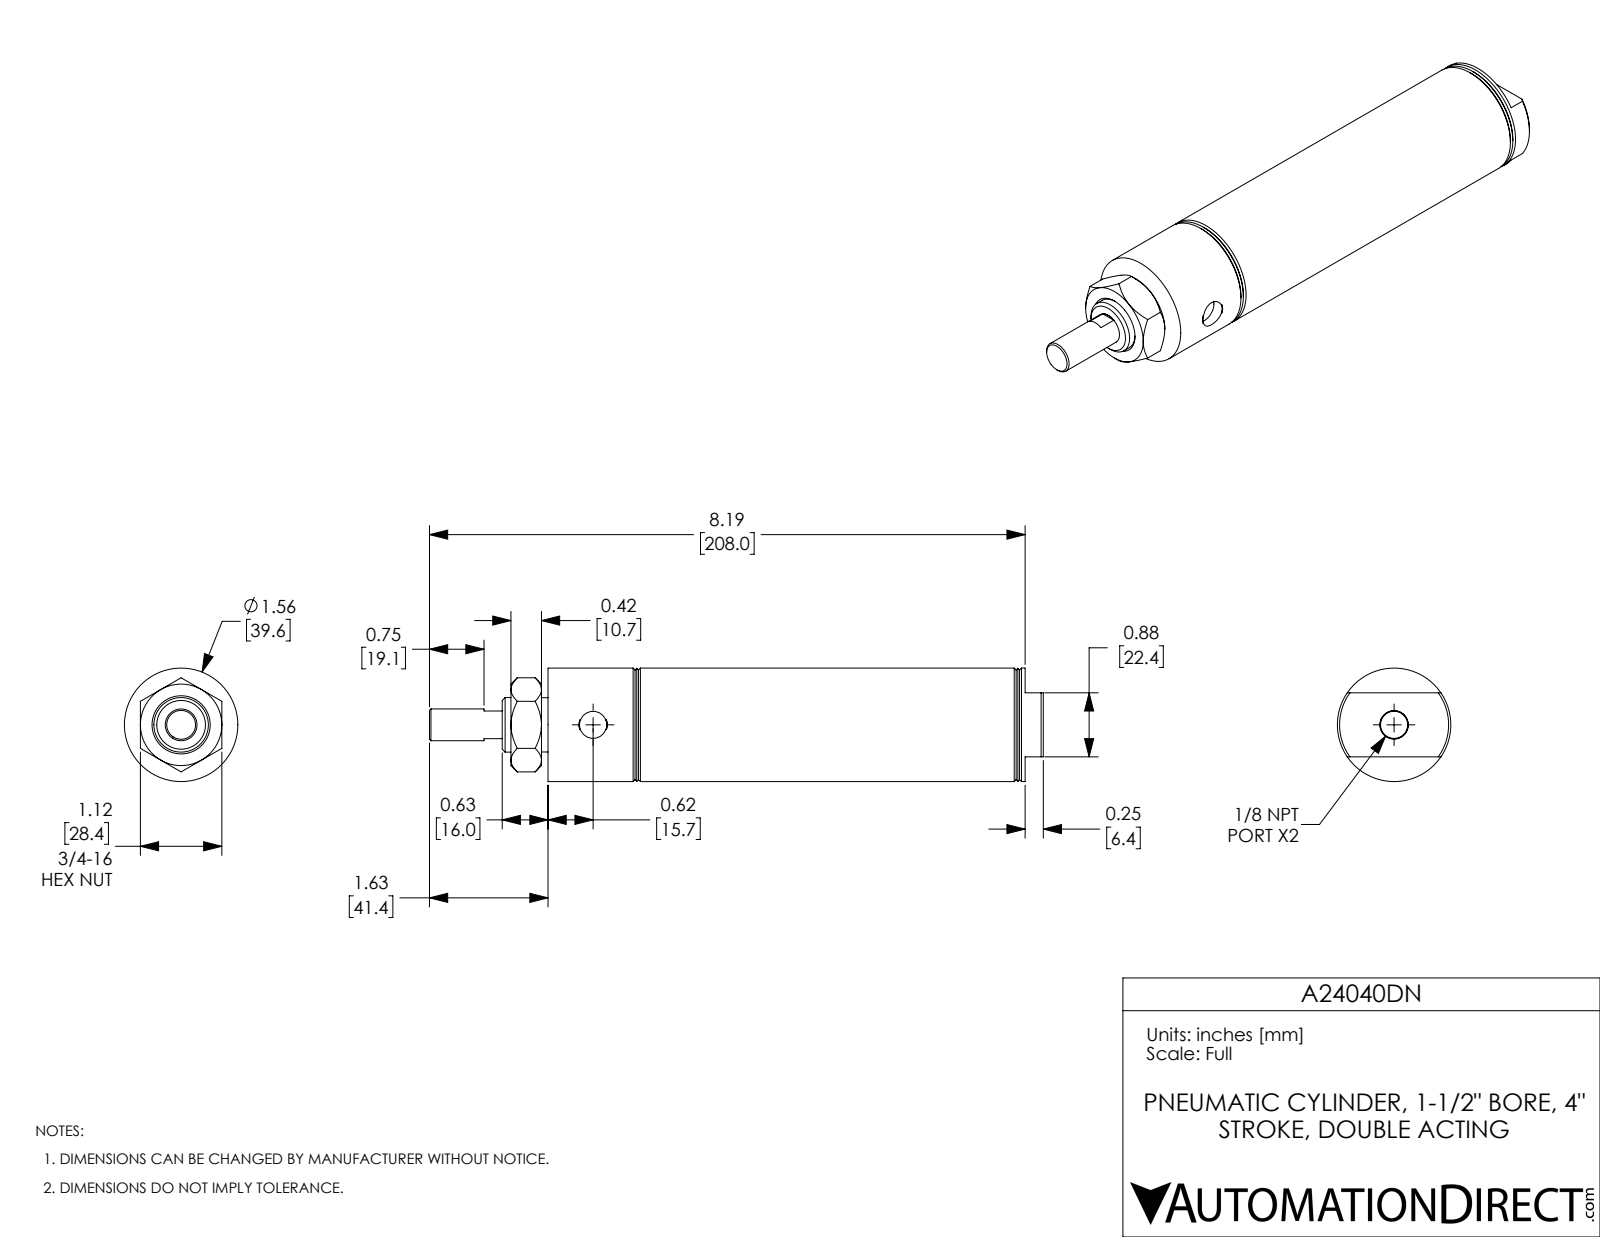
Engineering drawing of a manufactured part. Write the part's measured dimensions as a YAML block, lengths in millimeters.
part_name: "A24040DN_Mounting Nut_D-3556; A24040DN-Rod; A24040DN-MainBody; A24040DN"
step_written_by: "SolidWorks 2017 (AUTOMOTIVE_DESIGN)"
units: millimeters
bodies: {solids: 3, faces: 104, planar: 32, cylindrical: 24, other: 48}
overall_size: [214.4, 39.6, 39.6]
volume: 115100
surface_area: 55210
round_holes:
  - {diameter: 9.5, count: 2}
  - {diameter: 11.1, count: 1}
  - {diameter: 19.1, count: 1}
  - {diameter: 38.1, count: 1}
round_bosses_or_shafts:
  - {diameter: 39.6, count: 1}
  - {diameter: 18.9, count: 1}
face_to_face_distances: [12.7, 114.3, 101.6, 148.3, 135.6, 34, 24.6, 37.3, 138.9, 173]
